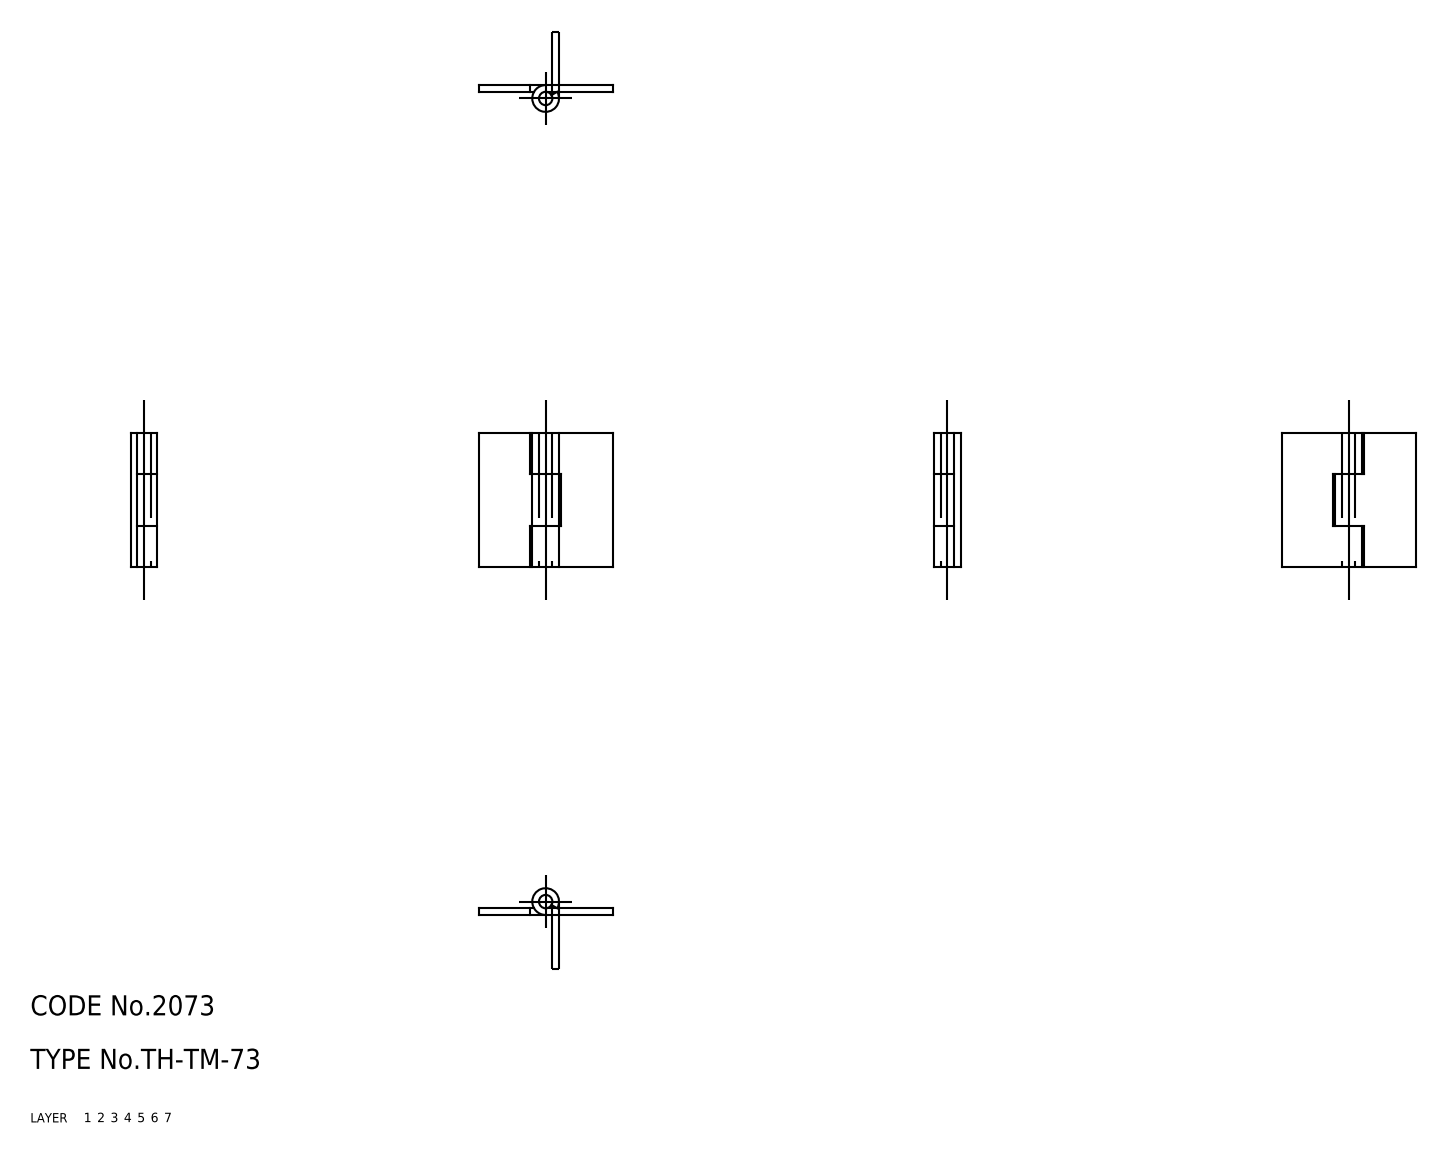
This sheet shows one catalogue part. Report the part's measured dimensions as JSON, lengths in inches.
{"part_name": "hinge piece_B; hinge piece_A; shaft; TH_TM_73_25311_36", "step_written_by": "CADfix (AUTOMOTIVE_DESIGN)", "units": "inches", "bodies": {"solids": 3, "faces": 30, "planar": 0, "cylindrical": 0, "other": 30}, "overall_size": [0.787, 0.787, 0.157], "volume_in3": 0.035, "surface_area_in2": 2.052}
